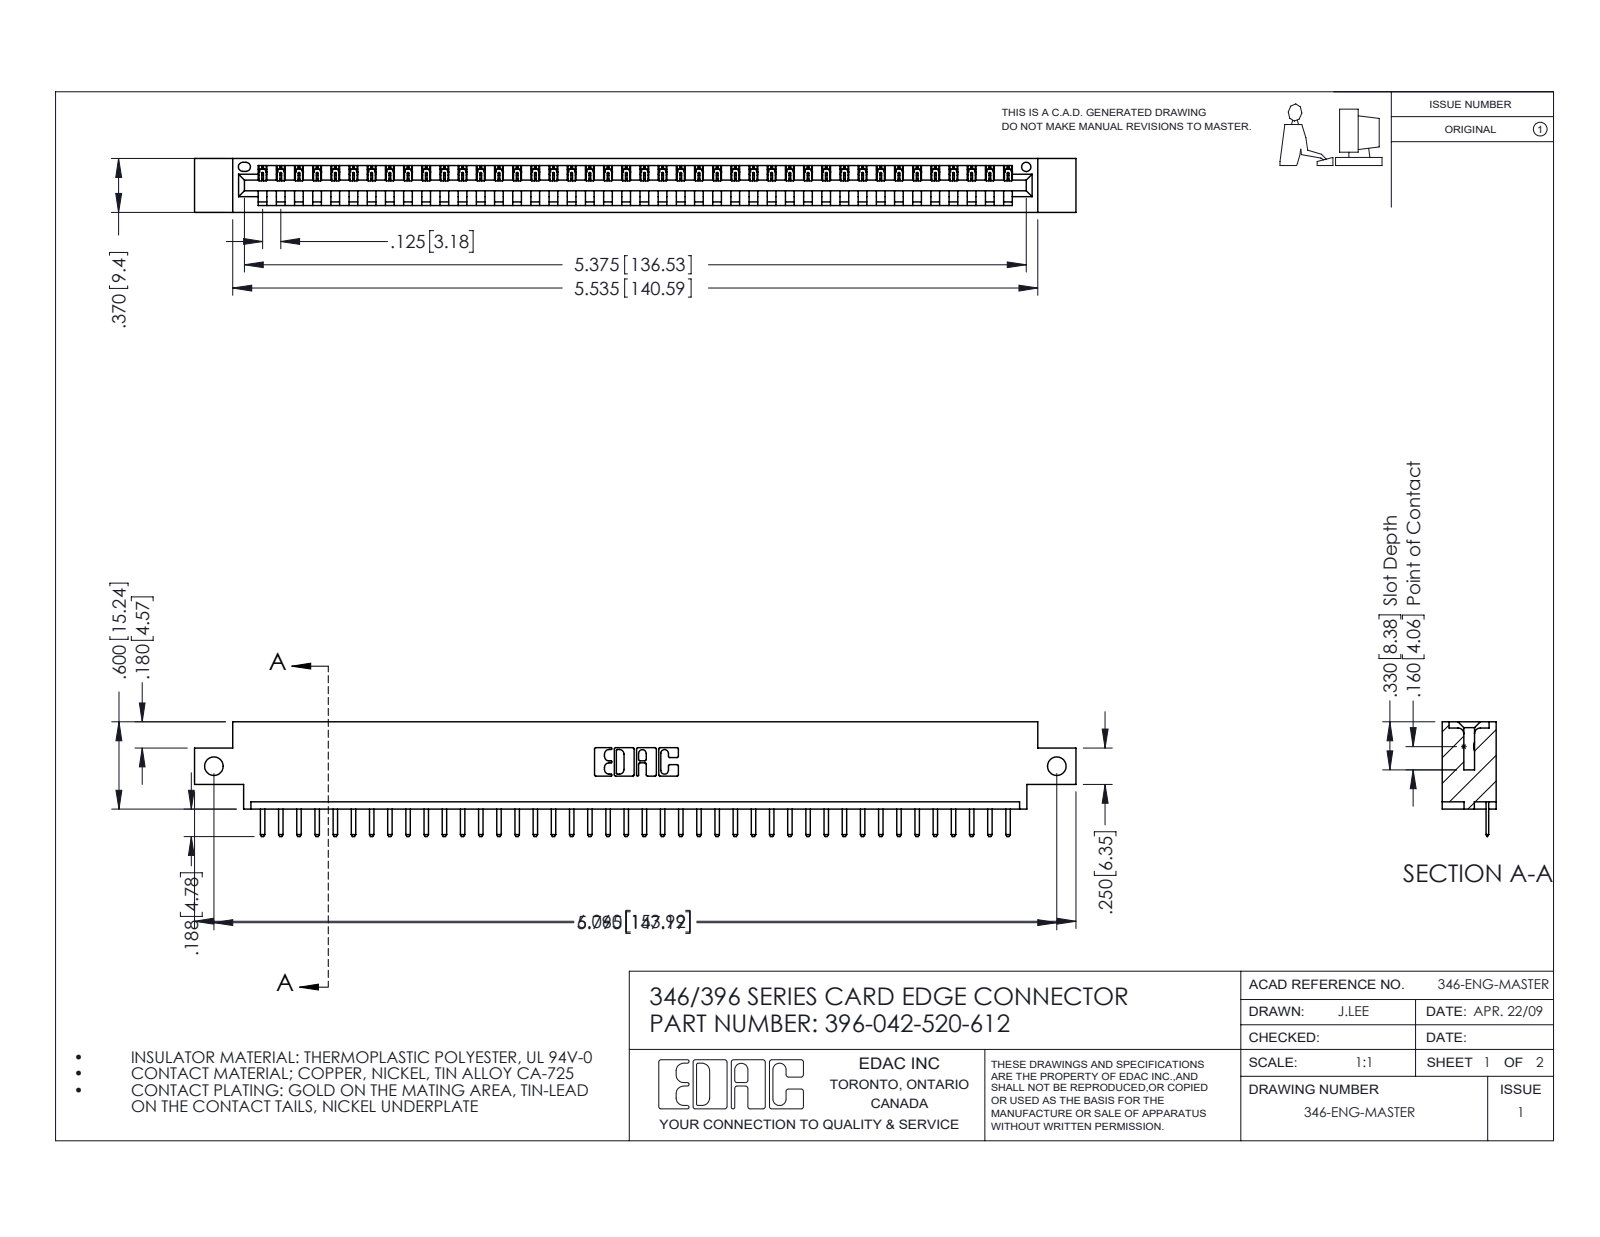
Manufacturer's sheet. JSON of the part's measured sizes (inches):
{"part_name": "345-292-001_345-293-120; 346 Part_0.170 Offset - Side Mount; 396-042-520-612", "step_written_by": "SolidWorks 2016 (CONFIG_CONTROL_DESIGN)", "units": "inches", "bodies": {"solids": 43, "faces": 2730, "planar": 1844, "cylindrical": 886, "other": 0}, "overall_size": [6.06, 0.788, 0.37], "volume_in3": 0.877, "surface_area_in2": 27.24, "round_holes": [[0.128, 2], [0.064, 1]], "partial_cylinders_radius": [[0.01, 86], [0.006, 84], [0.01, 22], [0.007, 6], [0.031, 6], [0.026, 3], [0.031, 2], [0.04, 2]], "face_to_face_distances": [0.048, 0.322, 0.37, 0.25, 0.148, 0.222, 0.1, 0.174, 0.072, 0.298], "hole_center_spacings": [5.795]}
